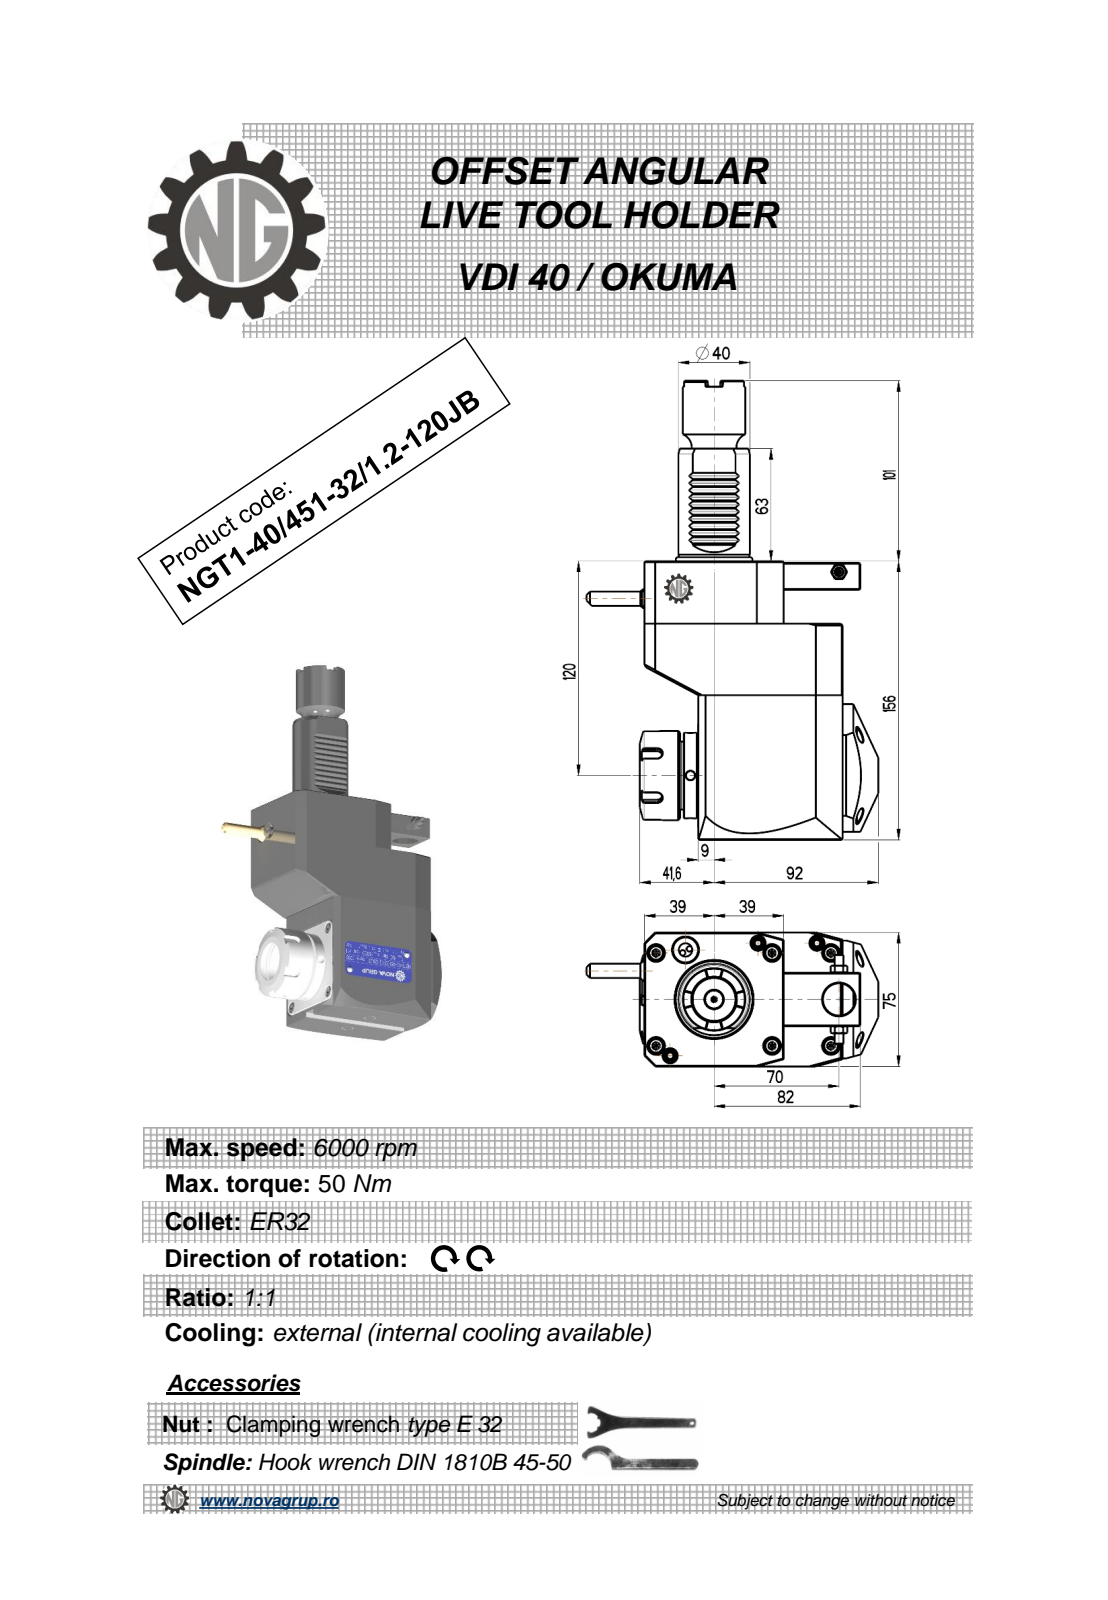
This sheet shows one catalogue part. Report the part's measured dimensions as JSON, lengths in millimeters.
{"part_name": "NGT1_40_451_32_1_2_120JB", "step_written_by": "PRO/ENGINEER BY PARAMETRIC TECHNOLOGY CORPORATION, 2010280 (CONFIG_CONTROL_DESIGN)", "units": "millimeters", "bodies": {"solids": 1, "faces": 477, "planar": 217, "cylindrical": 95, "other": 165}, "overall_size": [257, 163.5, 76.6], "volume_mm3": 1226000, "surface_area_mm2": 93997, "round_holes": [[5, 3], [3, 1], [4.2, 1], [9.5, 1], [18, 1], [25, 1], [26.8, 1], [27, 1]], "round_bosses_or_shafts": [[50, 1], [48, 1], [41, 1], [40, 1], [35, 1], [26.58, 1], [10, 1], [8.96, 1]], "partial_cylinders_radius": [[0.26, 12], [0.3, 10], [0.2, 6], [3, 5], [0.5, 1], [40, 1]], "face_to_face_distances": [75, 156, 111, 30, 121, 35, 33, 81, 48, 78], "hole_center_spacings": [13.25, 20.93, 70, 83.25, 100.28, 112.5, 141.16]}
